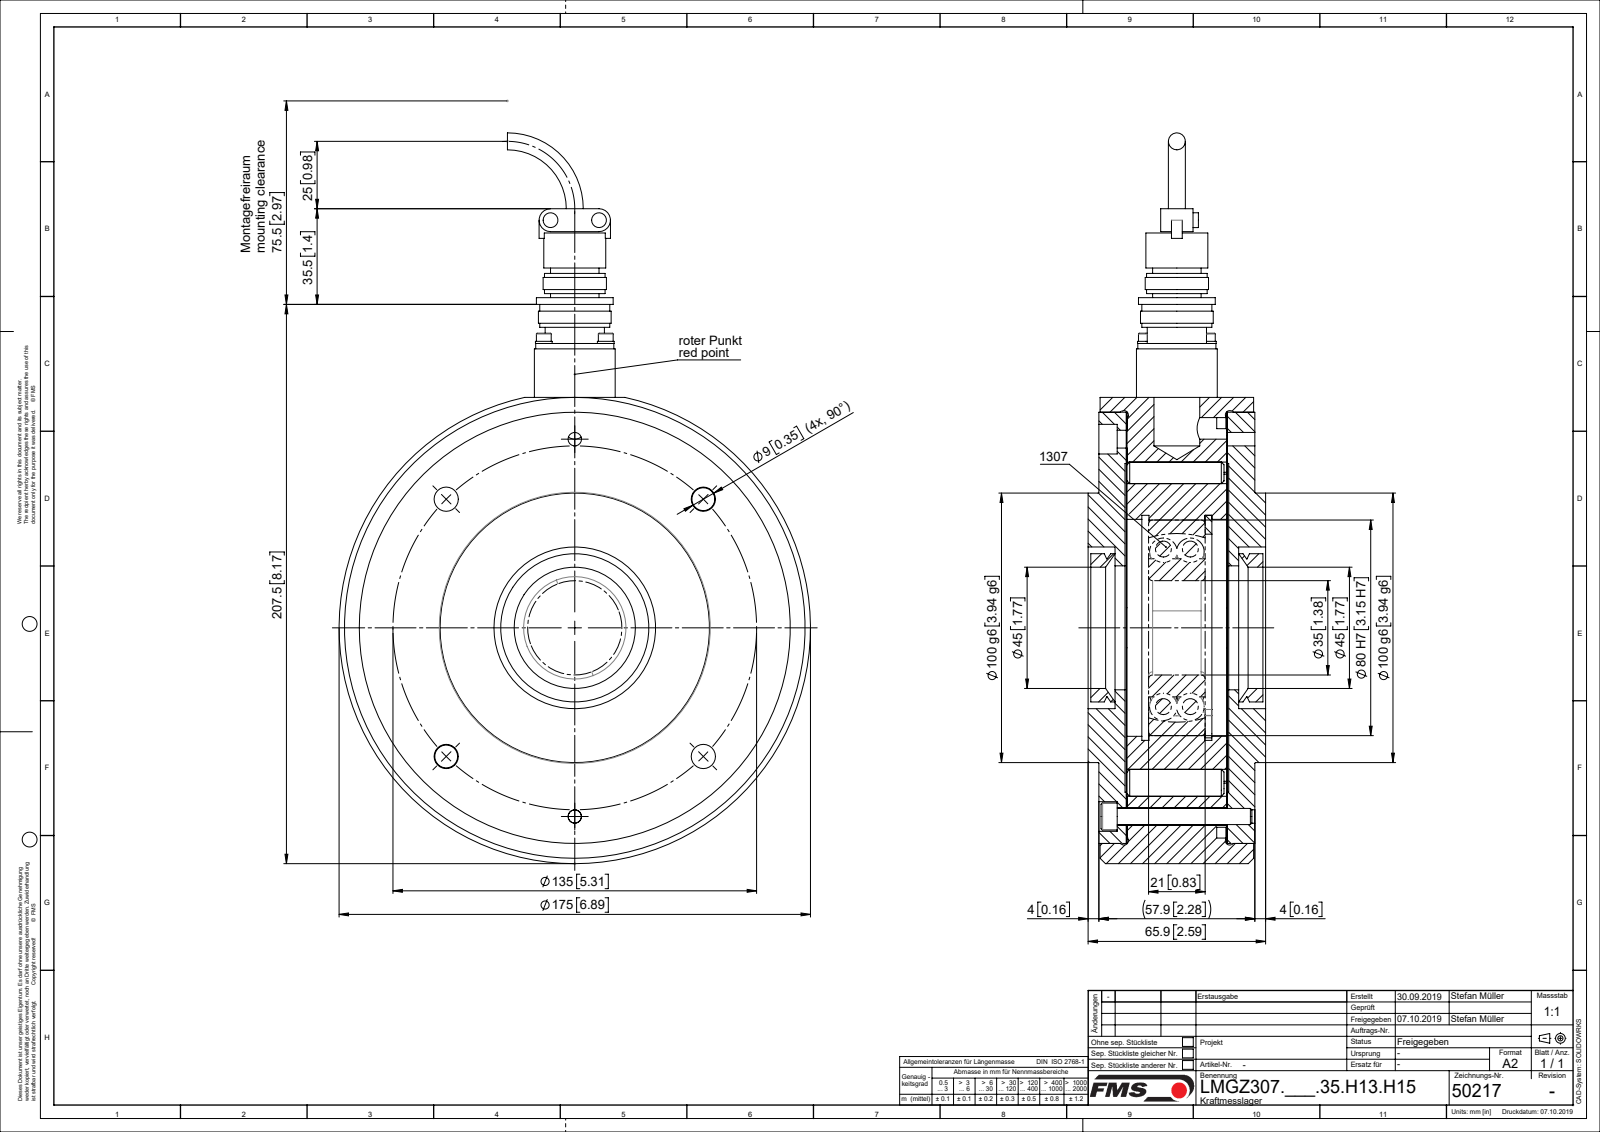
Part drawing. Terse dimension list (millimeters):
name: ZEICHNUNG7; L50217; L4943004; TEIL1 (+8 more)
written by: Mechanical Desktop 2007 (CONFIG_CONTROL_DESIGN)
unit: mm
bodies: 20 solids, 384 faces (99 planar, 229 cylindrical, 56 other)
size: 271.15 × 175 × 65.9
volume: 1 290 000 mm³; area: 266 603 mm²
holes: 4× ⌀2.6, 4× ⌀3.2, 4× ⌀3.4, 4× ⌀9, 2× ⌀5, 2× ⌀6.6, 2× ⌀11, 1× ⌀23, 1× ⌀35, 1× ⌀44, 1× ⌀46, 1× ⌀60
bosses: 6× ⌀5.5, 4× ⌀6.2, 4× ⌀3, 4× ⌀2.5, 1× ⌀175, 1× ⌀160, 1× ⌀100, 1× ⌀54
rounds: 2× R4.25, 2× R7.5
face distances: 37.25, 10.2, 10.45, 47.45, 47.7, 37, 0.5, 38, 9.7, 48.2
hole spacings: 16.26, 23, 52.67, 67.5, 95.46, 127.04, 32.53, 70
